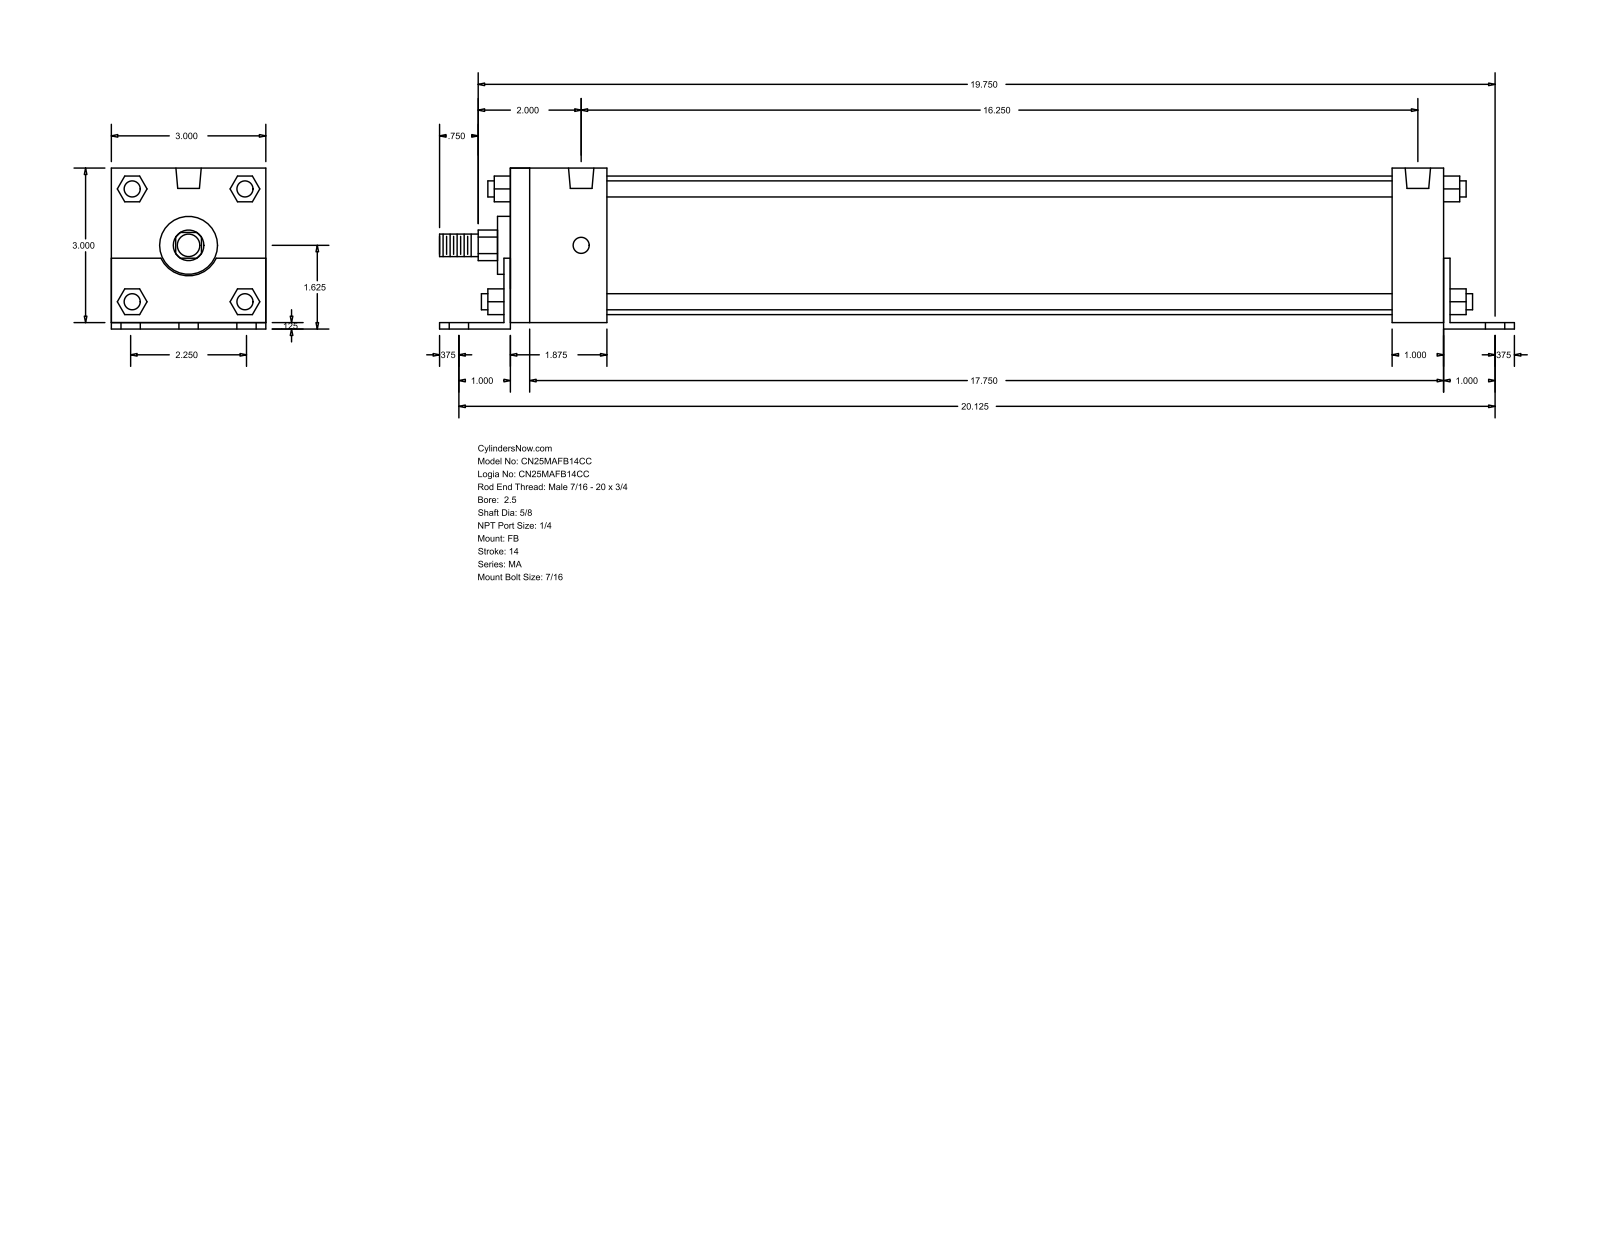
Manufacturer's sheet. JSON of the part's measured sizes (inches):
{"part_name": "MA_FB__0250_0.625", "step_written_by": "GSSL Pune (CONFIG_CONTROL_DESIGN)", "units": "inches", "bodies": {"solids": 0, "faces": 140, "planar": 105, "cylindrical": 35, "other": 0}, "overall_size": [20.875, 3.125, 3], "round_holes": [[0.437, 6], [0.313, 4], [0.492, 2]], "round_bosses_or_shafts": [[0.313, 4], [2.69, 1], [1.125, 1], [0.625, 1], [0.437, 1]], "partial_cylinders_radius": [[0.297, 1], [0.593, 1]], "face_to_face_distances": [3, 0.125, 3.125, 0.125, 18.25, 18.125, 1.125, 1.875, 1, 18.375], "hole_center_spacings": [1.125, 20.157, 20.125, 1.875, 2.25, 2.628, 16.25, 17.785]}
